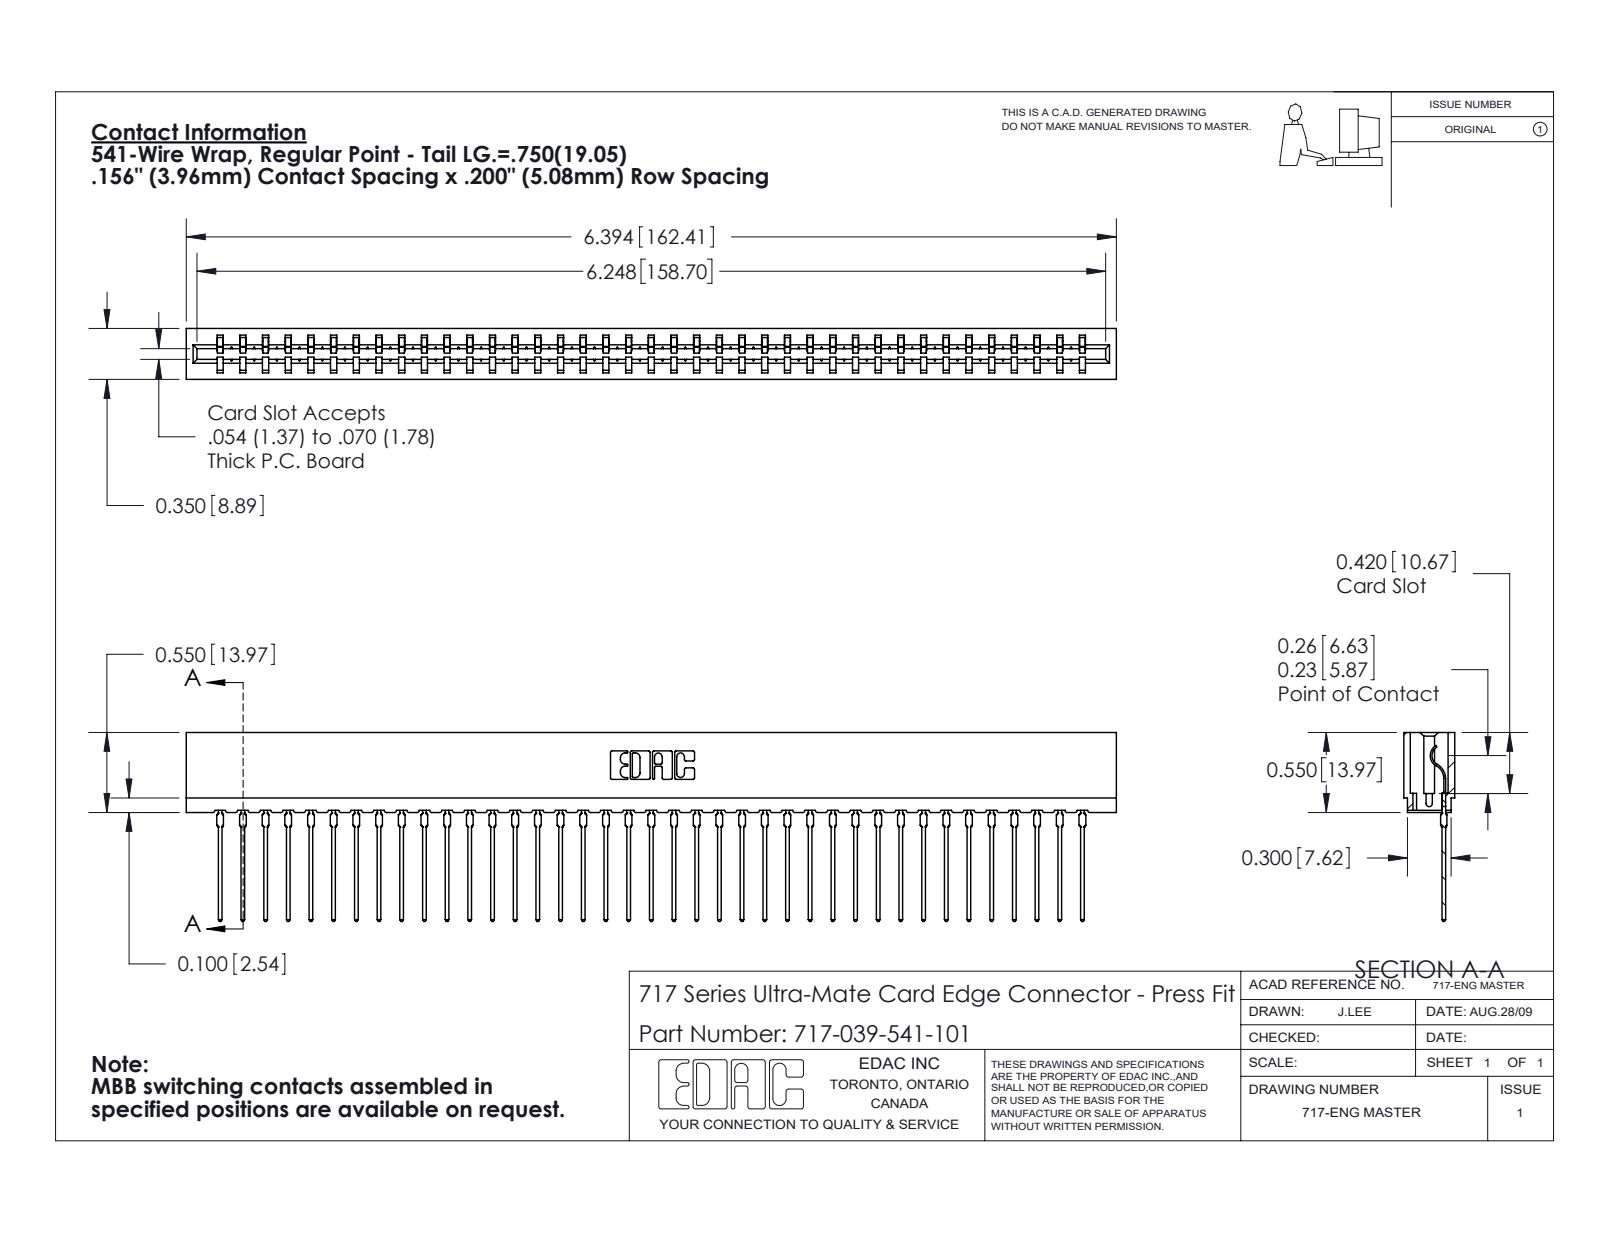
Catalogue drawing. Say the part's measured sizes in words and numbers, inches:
The part is named "717-039-541-101; 745-292-001_541; 717 Part_Insulator Option - 06". Its 3-D file was written by "SolidWorks 2020 (CONFIG_CONTROL_DESIGN)". It is 40 solids with 4501 faces: 2706 planar, 781 cylindrical and 1014 other. Overall it measures 6.394 by 1.299 by 0.35 inches. Its volume is 0.848 cubic inches and its surface area 31.47 square inches. Partial cylindrical surfaces (rounded edges, fillets, slot ends): 78 of radius 0.015, 78 of radius 0.021, 22 of radius 0.01, 6 of radius 0.007, 6 of radius 0.031, 4 of radius 0.005, 4 of radius 0.011, 3 of radius 0.026. The main face-to-face distances are 0.212, 0.138, 0.35, 0.063, 0.287, 0.076, 0.149, 0.074, 0.045, 0.305.
